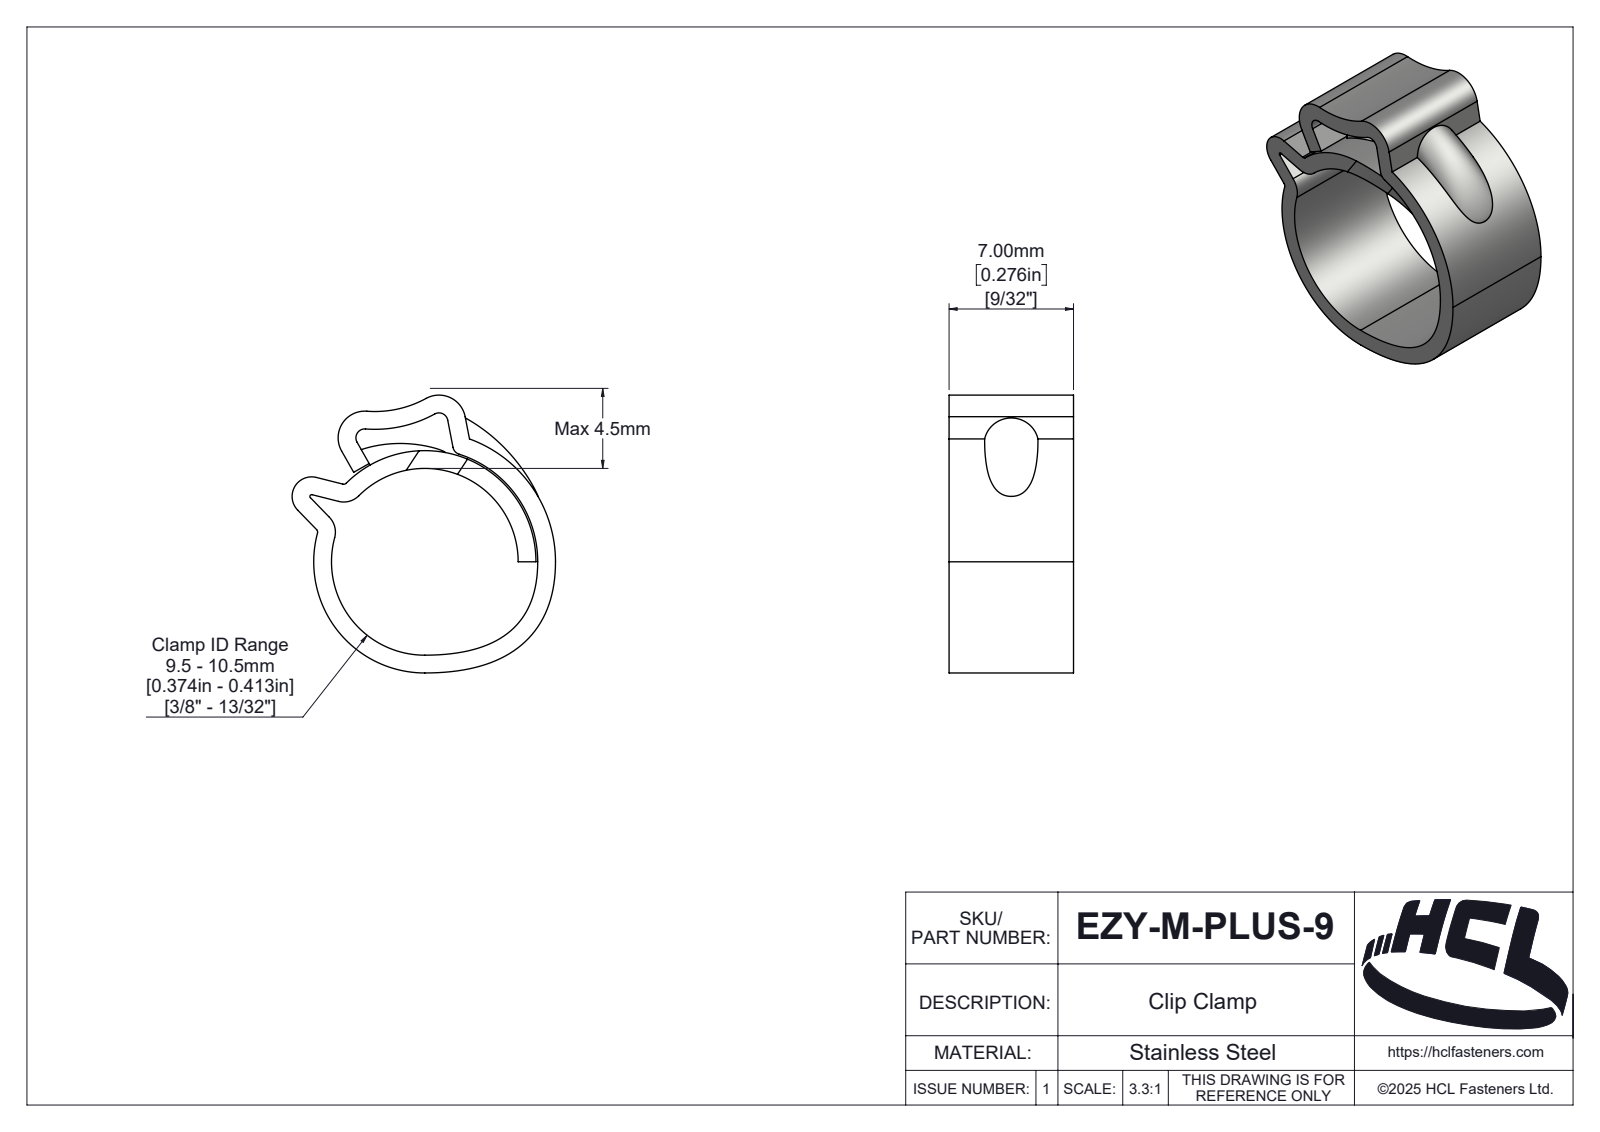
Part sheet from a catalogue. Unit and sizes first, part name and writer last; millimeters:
Units: millimetres
Overall size (bounding box): 15.62 × 14.81 × 7
Partial cylindrical surfaces — rounded edges, fillets, slot ends (radius × count): R0.5 ×3, R0.2 ×2, R1.2 ×2, R1.5 ×2, R10 ×2, R0.1 ×1, R0.23 ×1, R0.94 ×1
Main face-to-face distances: 7, 1
Volume: 411 mm³ · Surface area: 939 mm²
Bodies: 1 solid, 154 faces (17 planar, 74 cylindrical, 63 other)
Part name (STEP PRODUCT): EZY-M-PLUS-9
STEP written by: SolidWorks 2025 (AUTOMOTIVE_DESIGN)
